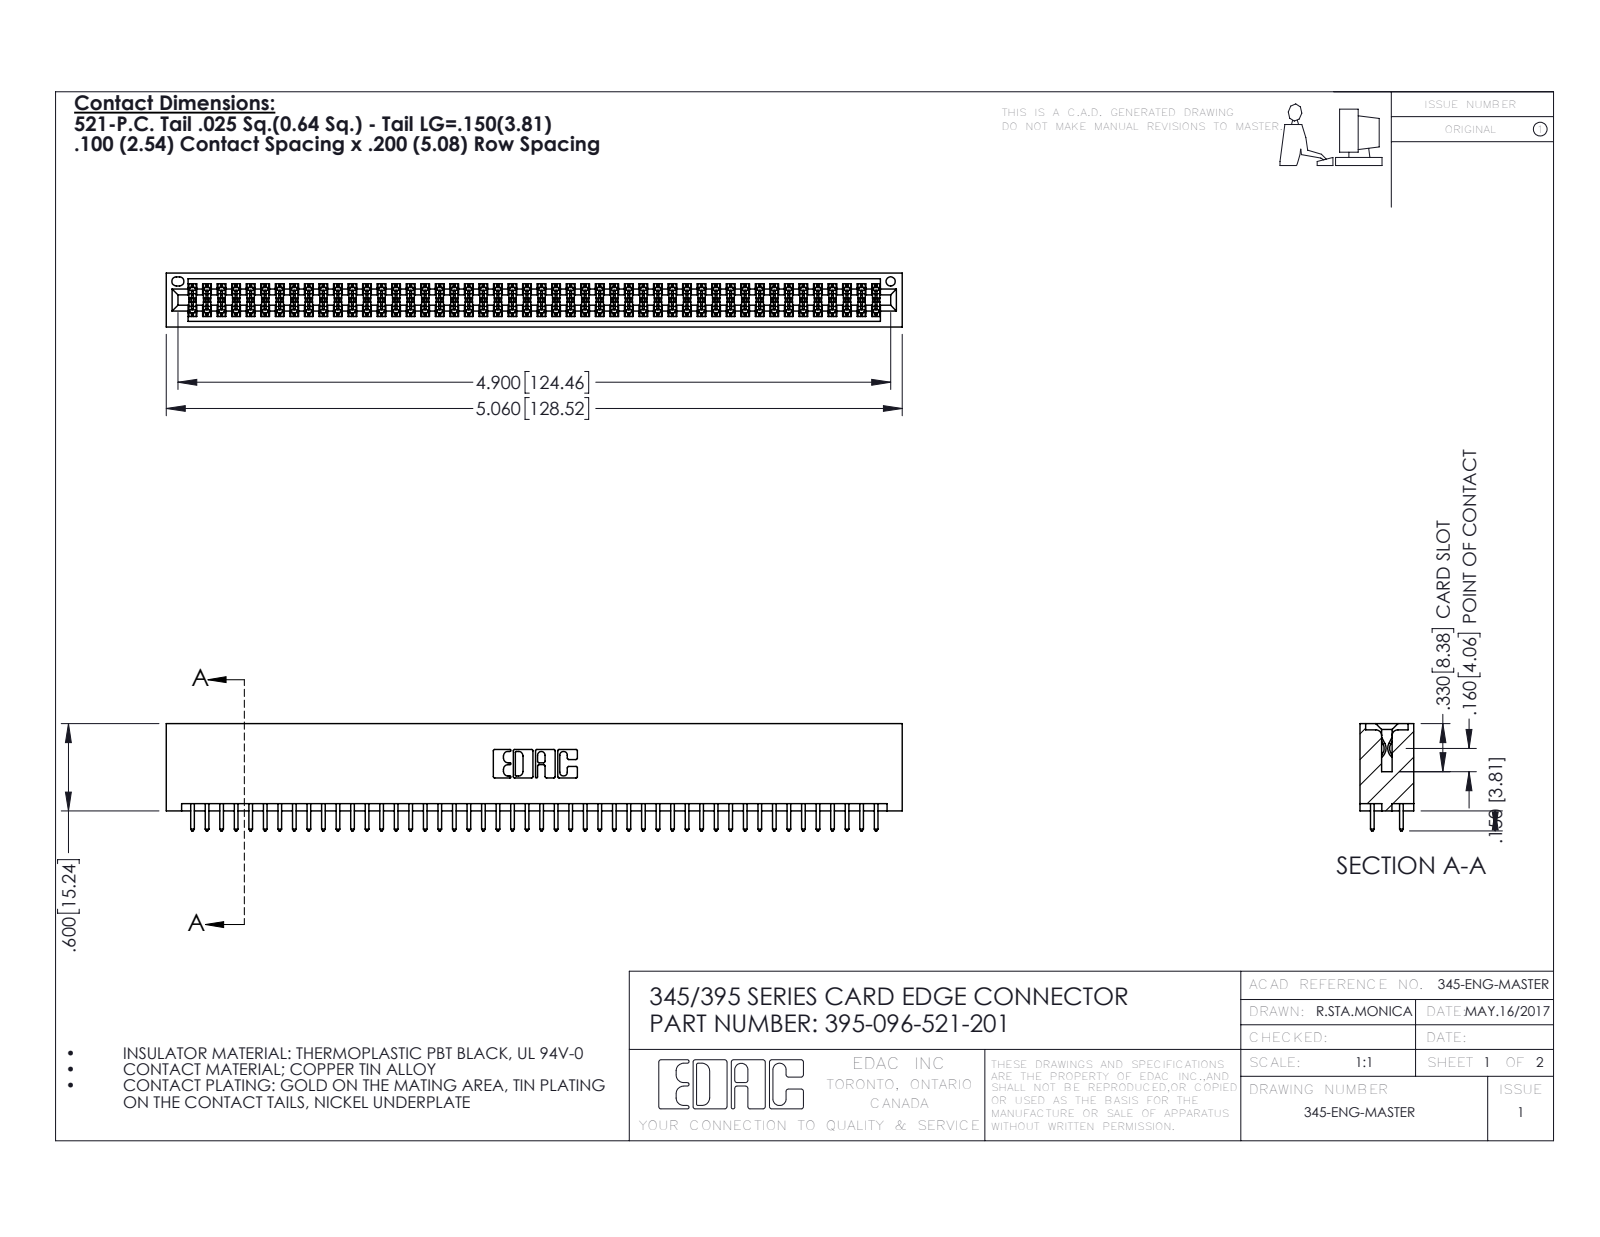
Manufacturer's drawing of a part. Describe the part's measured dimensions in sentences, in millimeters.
The part is named "345-292-001_345-293-121; 395-096-521-201; 345 Part_No Mounting Lugs". Its 3-D file was written by "SolidWorks 2016 (CONFIG_CONTROL_DESIGN)". It is 97 solids with 4918 faces: 3244 planar, 1674 cylindrical and 0 other. Overall it measures 128.5 by 18.7 by 9.4 millimeters. Its volume is 13 100 cubic millimeters and its surface area 19 550 square millimeters. Round holes: 1 of diameter 1.6. Partial cylindrical surfaces (rounded edges, fillets, slot ends): 144 of radius 0.2, 96 of radius 0.3, 22 of radius 0.3, 6 of radius 0.2, 6 of radius 0.8, 3 of radius 0.7, 2 of radius 0.4, 2 of radius 0.5. The main face-to-face distances are 7.6, 1.8, 5.1, 2.5, 6.9, 0.6, 9.4, 5.7, 4.4, 3.8.
